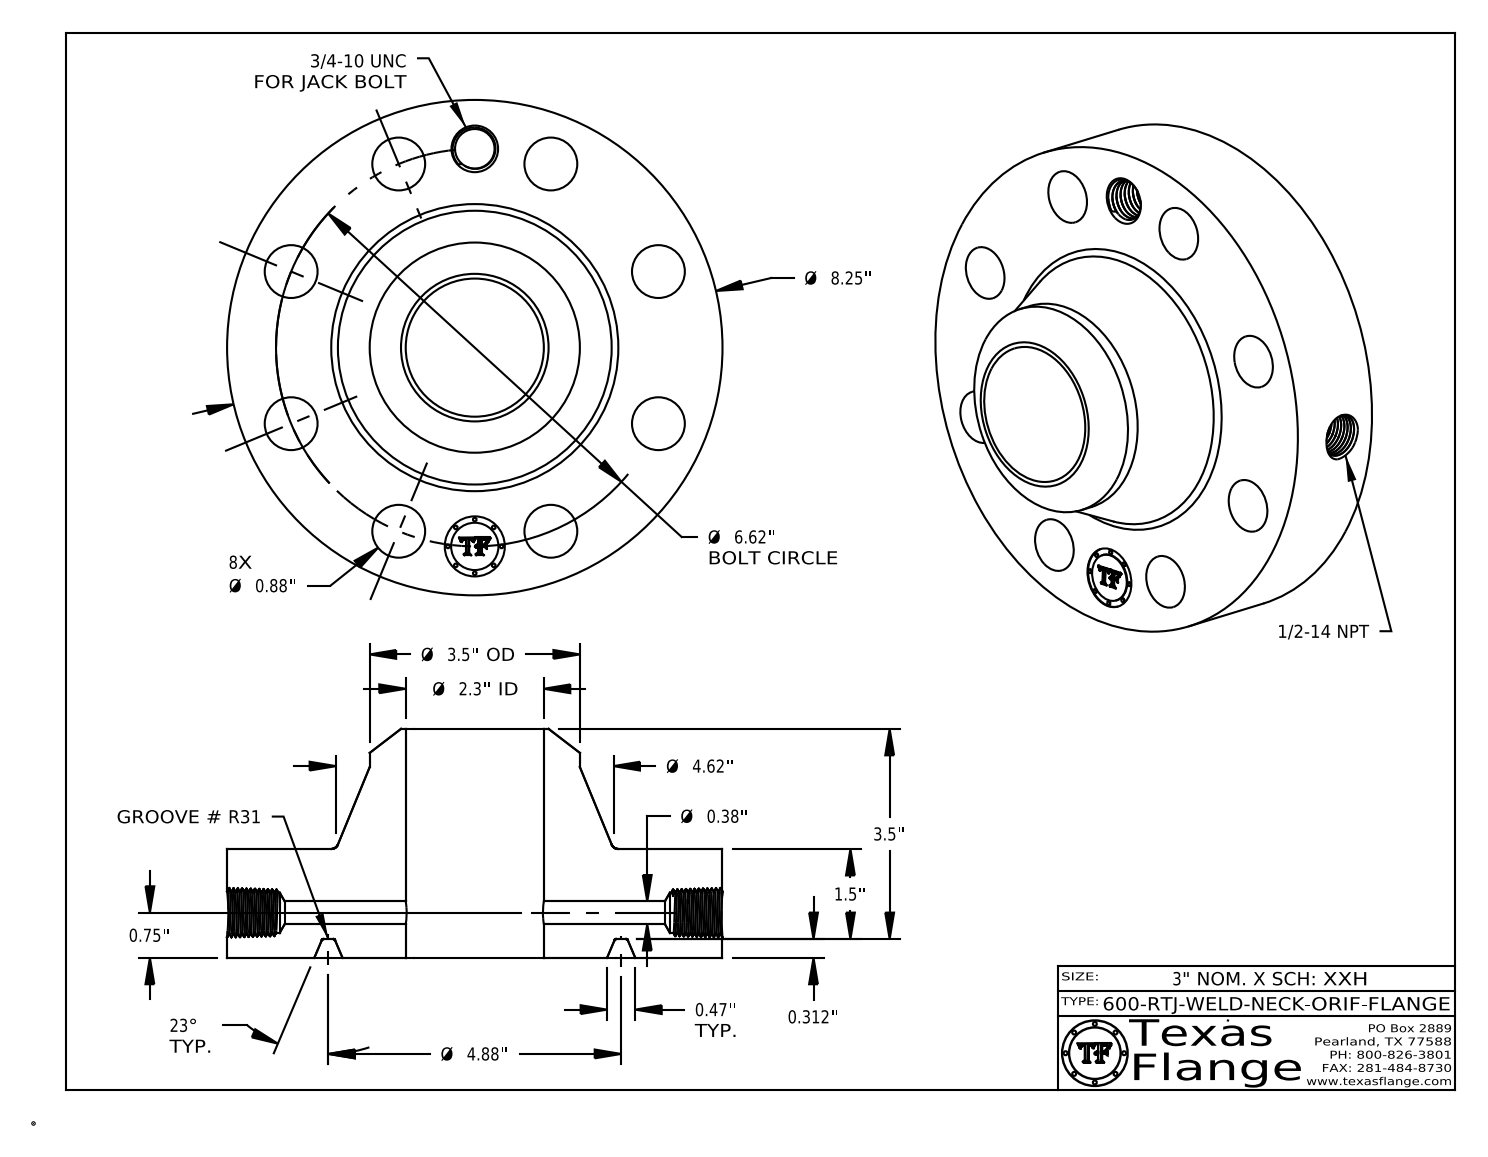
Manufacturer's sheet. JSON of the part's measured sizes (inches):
{"part_name": "600-RTJ-WELD-NECK", "step_written_by": "CATIA V5 STEP AP214 (AUTOMOTIVE_DESIGN)", "units": "inches", "bodies": {"solids": 1, "faces": 795, "planar": 370, "cylindrical": 96, "other": 329}, "overall_size": [8.25, 8.25, 3.812], "volume_in3": 91.54, "surface_area_in2": 241.1, "round_holes": [[0.88, 8], [0.375, 1], [0.656, 1], [0.672, 1], [1, 1], [2.3, 1]], "round_bosses_or_shafts": [[0.061, 8], [8.25, 1], [3.5, 1], [0.788, 1]], "face_to_face_distances": [1.812, 0.312, 1.5, 3.812, 3.5, 2, 0.015, 1.797, 1.485, 2.015], "hole_center_spacings": [3.31, 4.681, 6.116, 6.62, 1.291, 2.533, 2.533, 3.678]}
